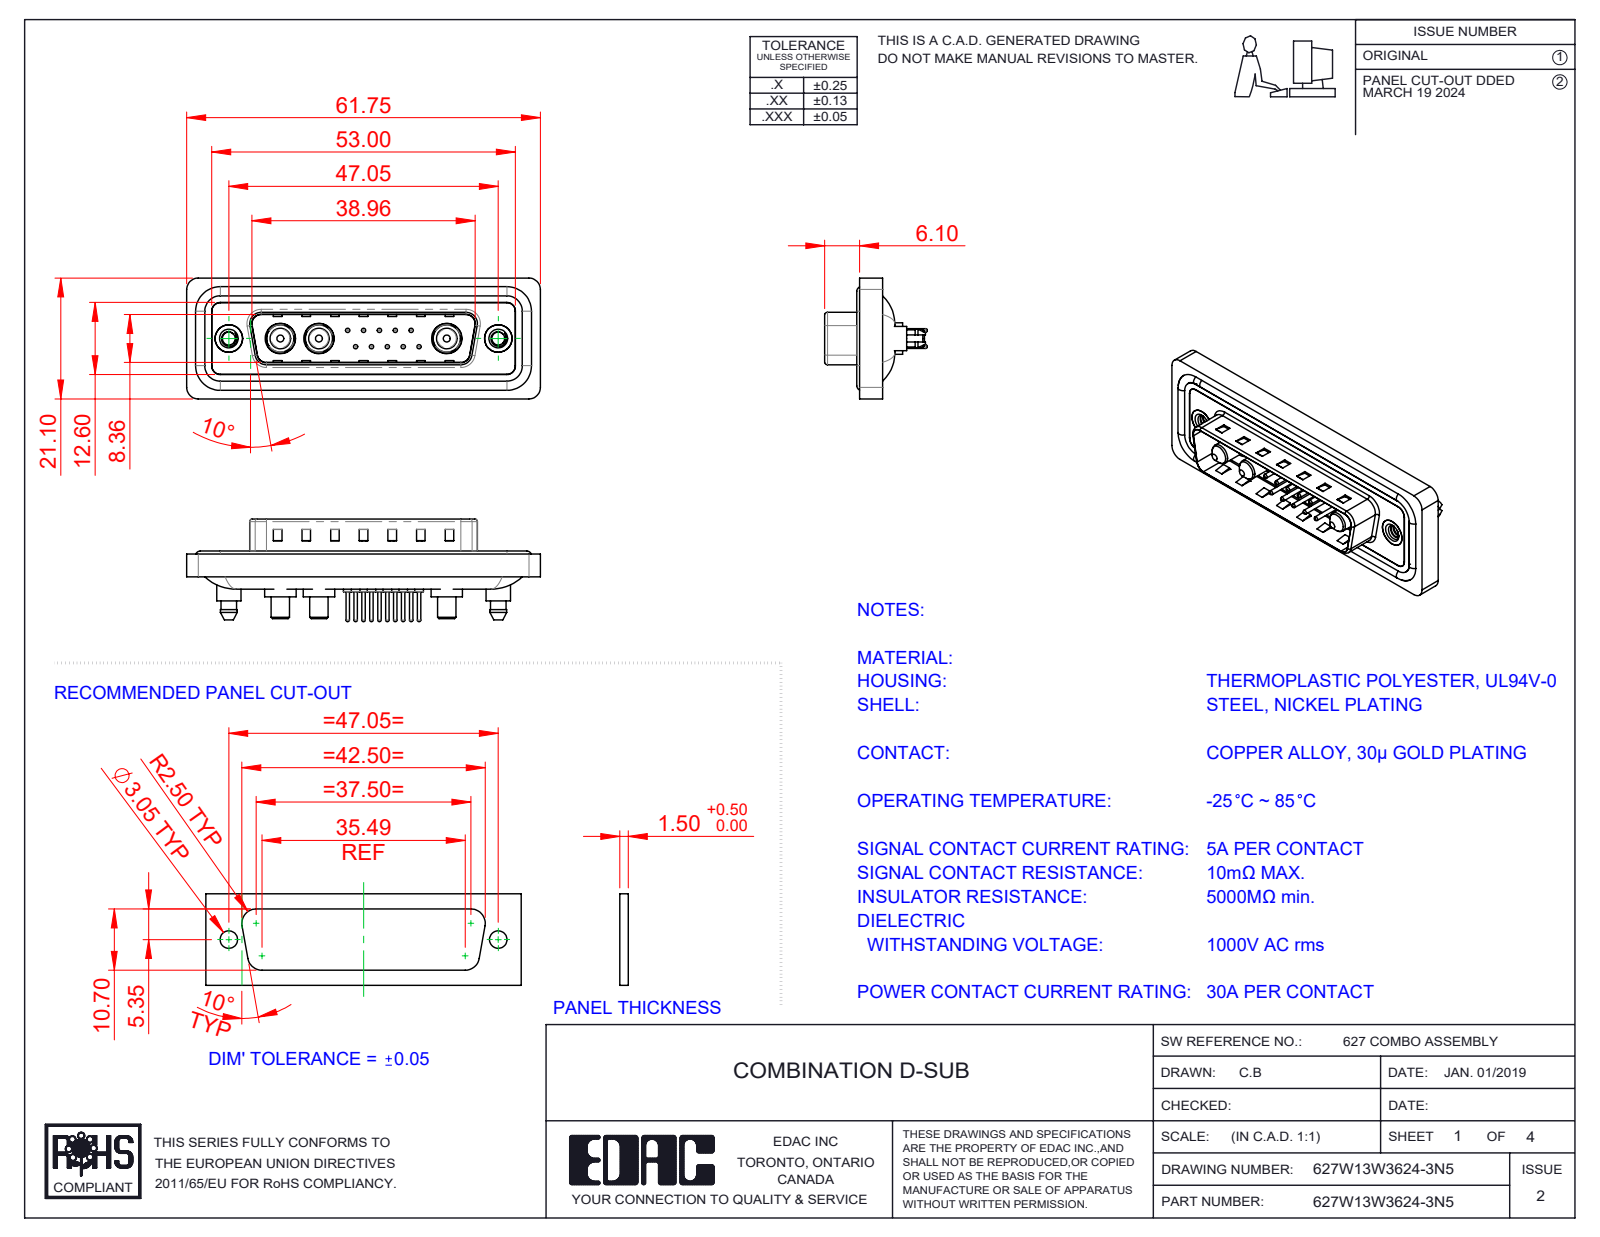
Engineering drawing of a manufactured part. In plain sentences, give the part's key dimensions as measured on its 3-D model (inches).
The part is named "627Combo Shell Rear_25 Contacts; 627Combo Contact Row 2_24; Power Pin_30A S; 627Combo Waterproof Housing_25 Contacts (+5 more)". Its 3-D file was written by "SolidWorks 2023 (CONFIG_CONTROL_DESIGN)". It is 23 solids with 1020 faces: 325 planar, 417 cylindrical and 278 other. Overall it measures 2.431 by 0.831 by 0.705 inches. Its volume is 0.457 cubic inches and its surface area 18.94 square inches. Round holes: 10 of diameter 0.03, 10 of diameter 0.063, 10 of diameter 0.079, 3 of diameter 0.191, 3 of diameter 0.209, 2 of diameter 0.089, 2 of diameter 0.157, 2 of diameter 0.189, 2 of diameter 0.197. Round bosses or shafts: 10 of diameter 0.059, 10 of diameter 0.024, 4 of diameter 0.063, 3 of diameter 0.217, 3 of diameter 0.205, 3 of diameter 0.187, 3 of diameter 0.148, 3 of diameter 0.142. Partial cylindrical surfaces (rounded edges, fillets, slot ends): 24 of radius 0.059, 18 of radius 0.079, 10 of radius 0.063, 8 of radius 0.02, 4 of radius 0.01, 4 of radius 0.024, 4 of radius 0.026, 4 of radius 0.035. The main face-to-face distances are 0.016, 0.059, 0.043, 0.063, 0.02, 0.122, 0.114, 0.032, 0.377, 0.161. The hole center spacings are 0.124, 0.109, 0.198, 0.218, 0.295, 0.198, 0.327, 0.398.
